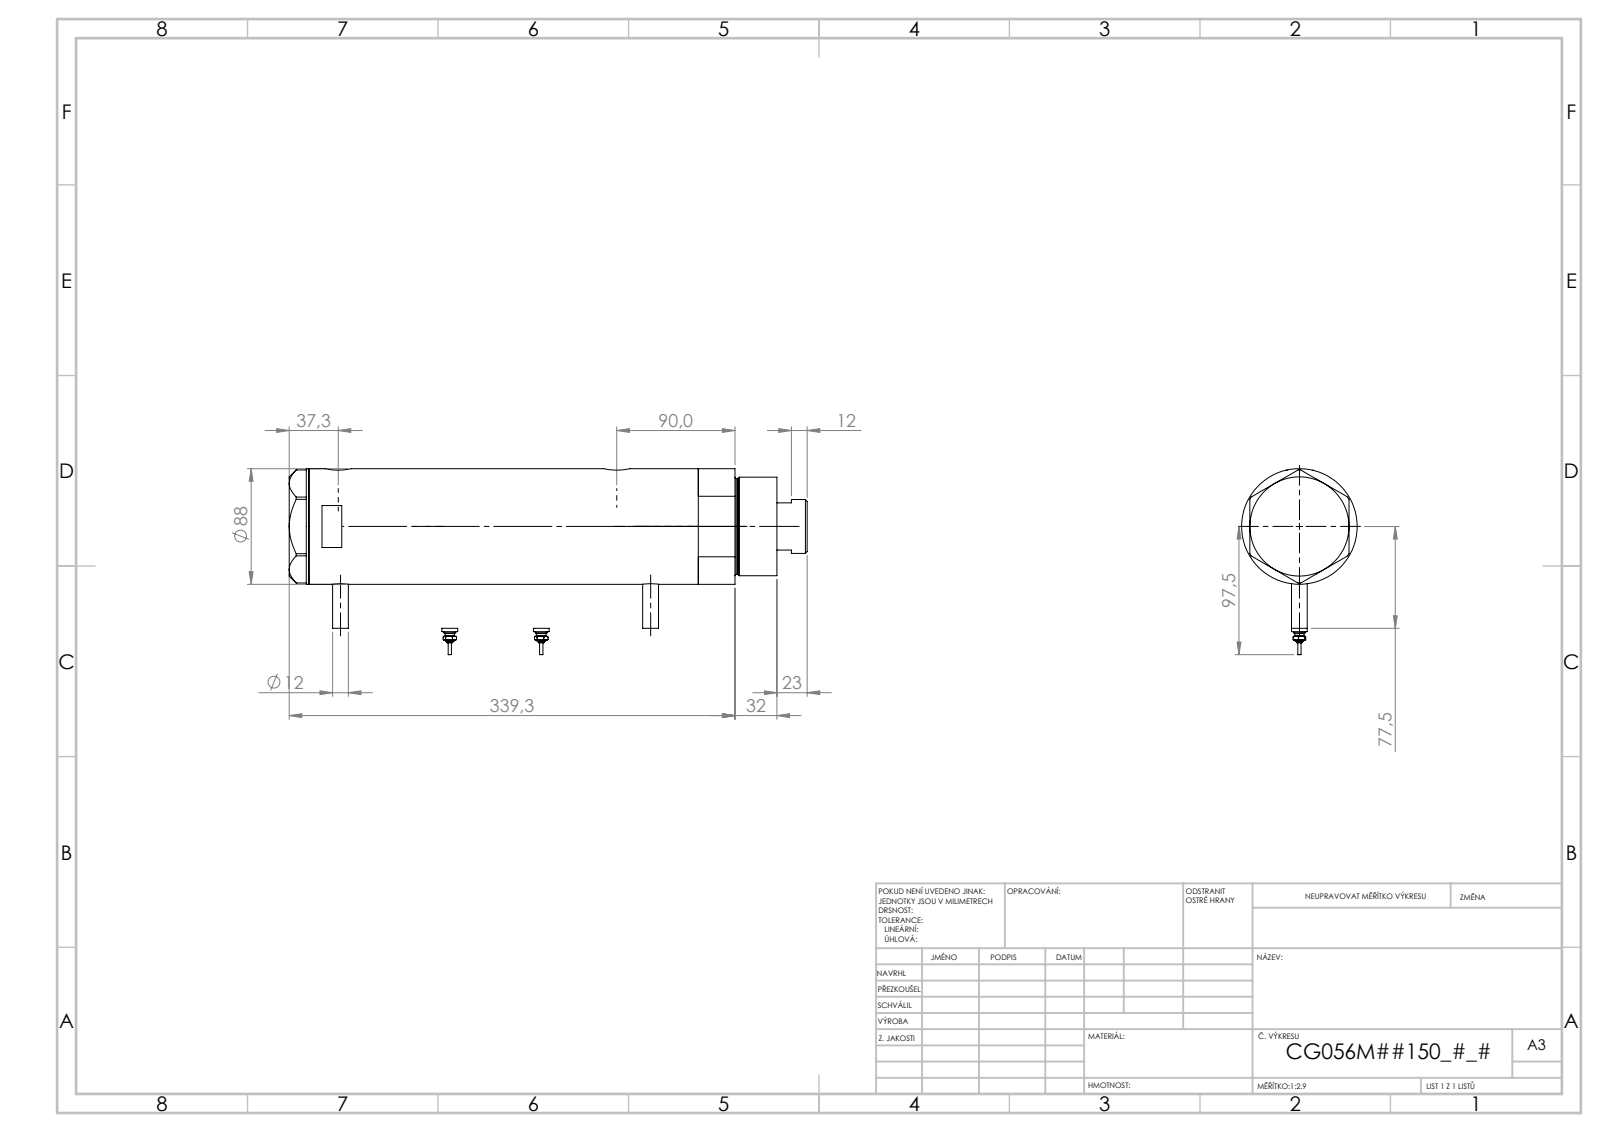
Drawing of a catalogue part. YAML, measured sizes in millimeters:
part_name: "V270CG_BACK; V270CG_VC; V270CG_MIDDLE; V270CG_FRONT (+1 more)"
step_written_by: "SolidWorks 2019 (CONFIG_CONTROL_DESIGN)"
units: millimeters
bodies: {solids: 6, faces: 232, planar: 81, cylindrical: 77, other: 74}
overall_size: [374.47, 120.3, 88]
volume: 1915000
surface_area: 269857
round_holes:
  - {diameter: 5, count: 2}
  - {diameter: 12.5, count: 2}
  - {diameter: 13.16, count: 2}
  - {diameter: 20, count: 2}
  - {diameter: 14.5, count: 1}
  - {diameter: 42, count: 1}
  - {diameter: 43.5, count: 1}
  - {diameter: 56, count: 1}
  - {diameter: 60, count: 1}
  - {diameter: 80, count: 1}
round_bosses_or_shafts:
  - {diameter: 12, count: 2}
  - {diameter: 9, count: 2}
  - {diameter: 7, count: 2}
  - {diameter: 4.34, count: 2}
  - {diameter: 2.4, count: 2}
  - {diameter: 88, count: 1}
  - {diameter: 75, count: 1}
  - {diameter: 73, count: 1}
face_to_face_distances: [224.4, 26, 198.4, 15, 41, 239.4, 336.47, 351.47, 310.47, 112.07]
hole_center_spacings: [1.7, 25.8, 200.3, 202, 226.1, 227.8]
